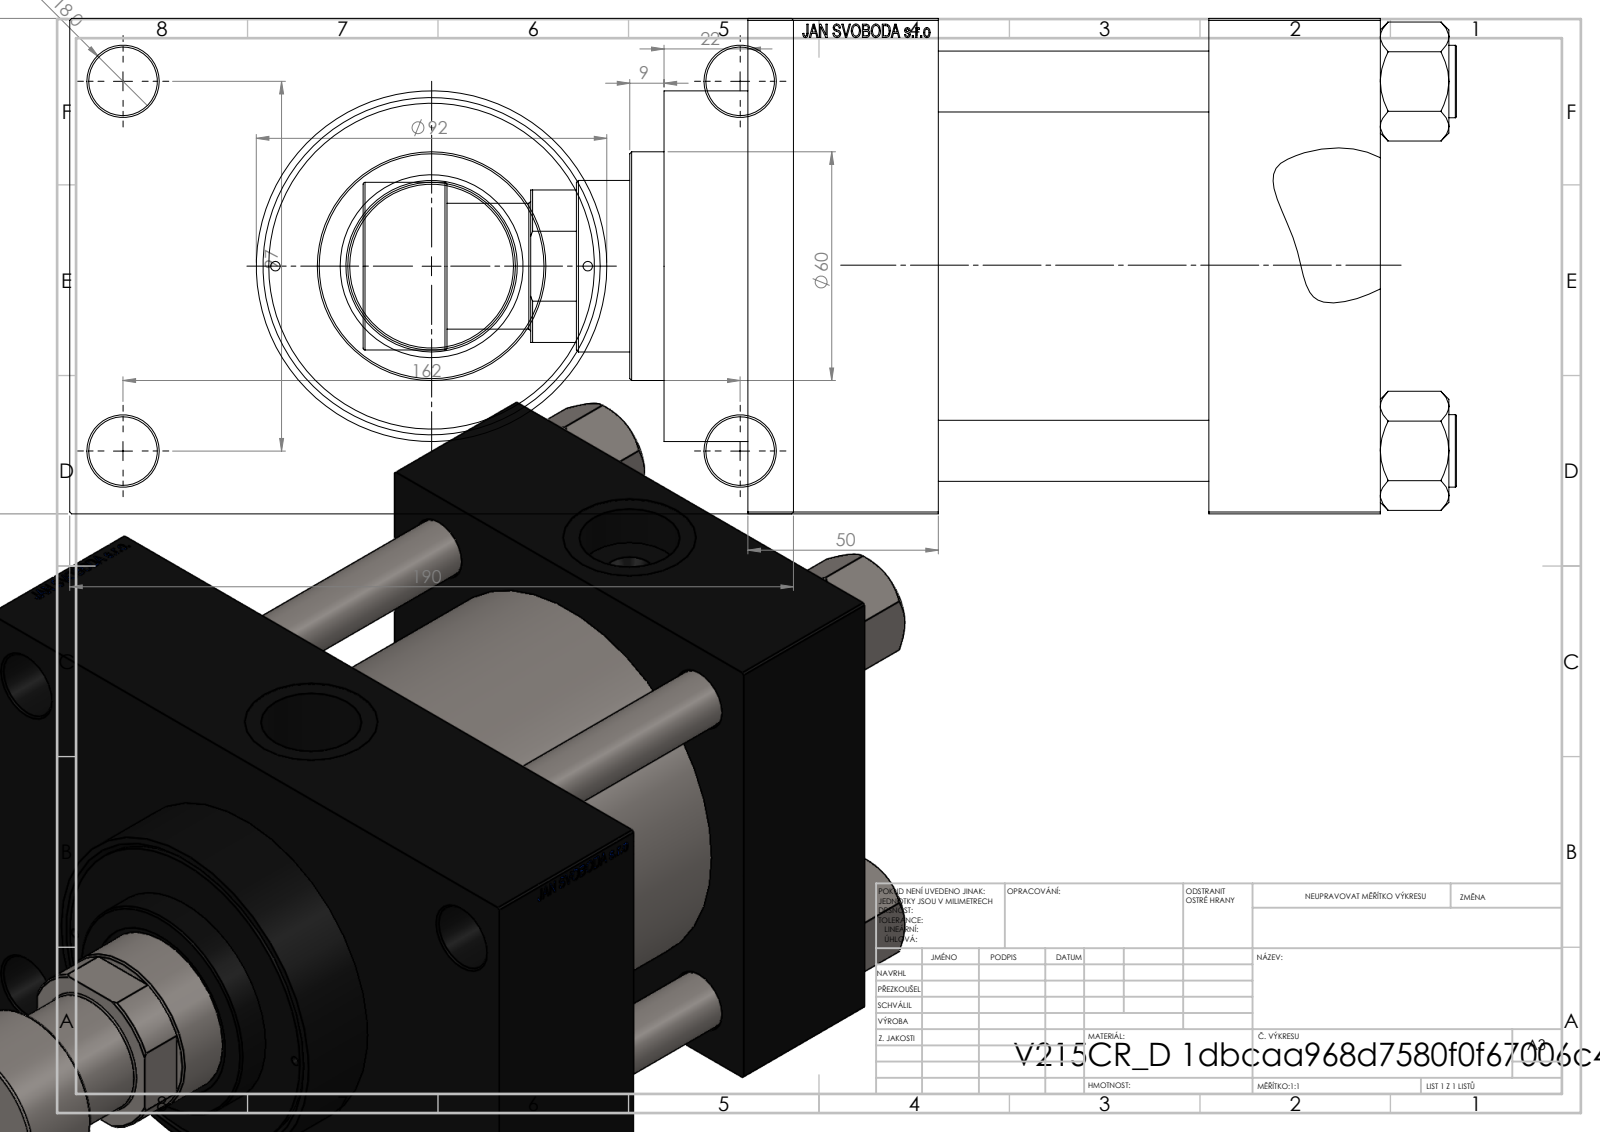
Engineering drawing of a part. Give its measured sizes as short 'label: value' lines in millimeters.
name: V215CR_D_Body; V215CR_VCP_D; NUT_M5_D; V215CR_ROD_END_F (+2 more)
written by: SolidWorks 2019 (CONFIG_CONTROL_DESIGN)
unit: mm
bodies: 12 solids, 1173 faces (550 planar, 97 cylindrical, 526 other)
size: 287 × 190 × 130
volume: 2 659 000 mm³; area: 360 618 mm²
holes: 4× ⌀16, 4× ⌀18, 2× ⌀2.5, 2× ⌀7, 2× ⌀26.44, 2× ⌀35, 1× ⌀31.5, 1× ⌀45, 1× ⌀48, 1× ⌀76, 1× ⌀85.5, 1× ⌀100
bosses: 4× ⌀19, 1× ⌀106, 1× ⌀92, 1× ⌀60, 1× ⌀44, 1× ⌀33
face distances: 130, 116, 45, 71, 166, 121, 50, 30, 160, 70
hole spacings: 32.55, 49.02, 62.87, 68.52, 94.41, 96.9, 101.73, 102.27
